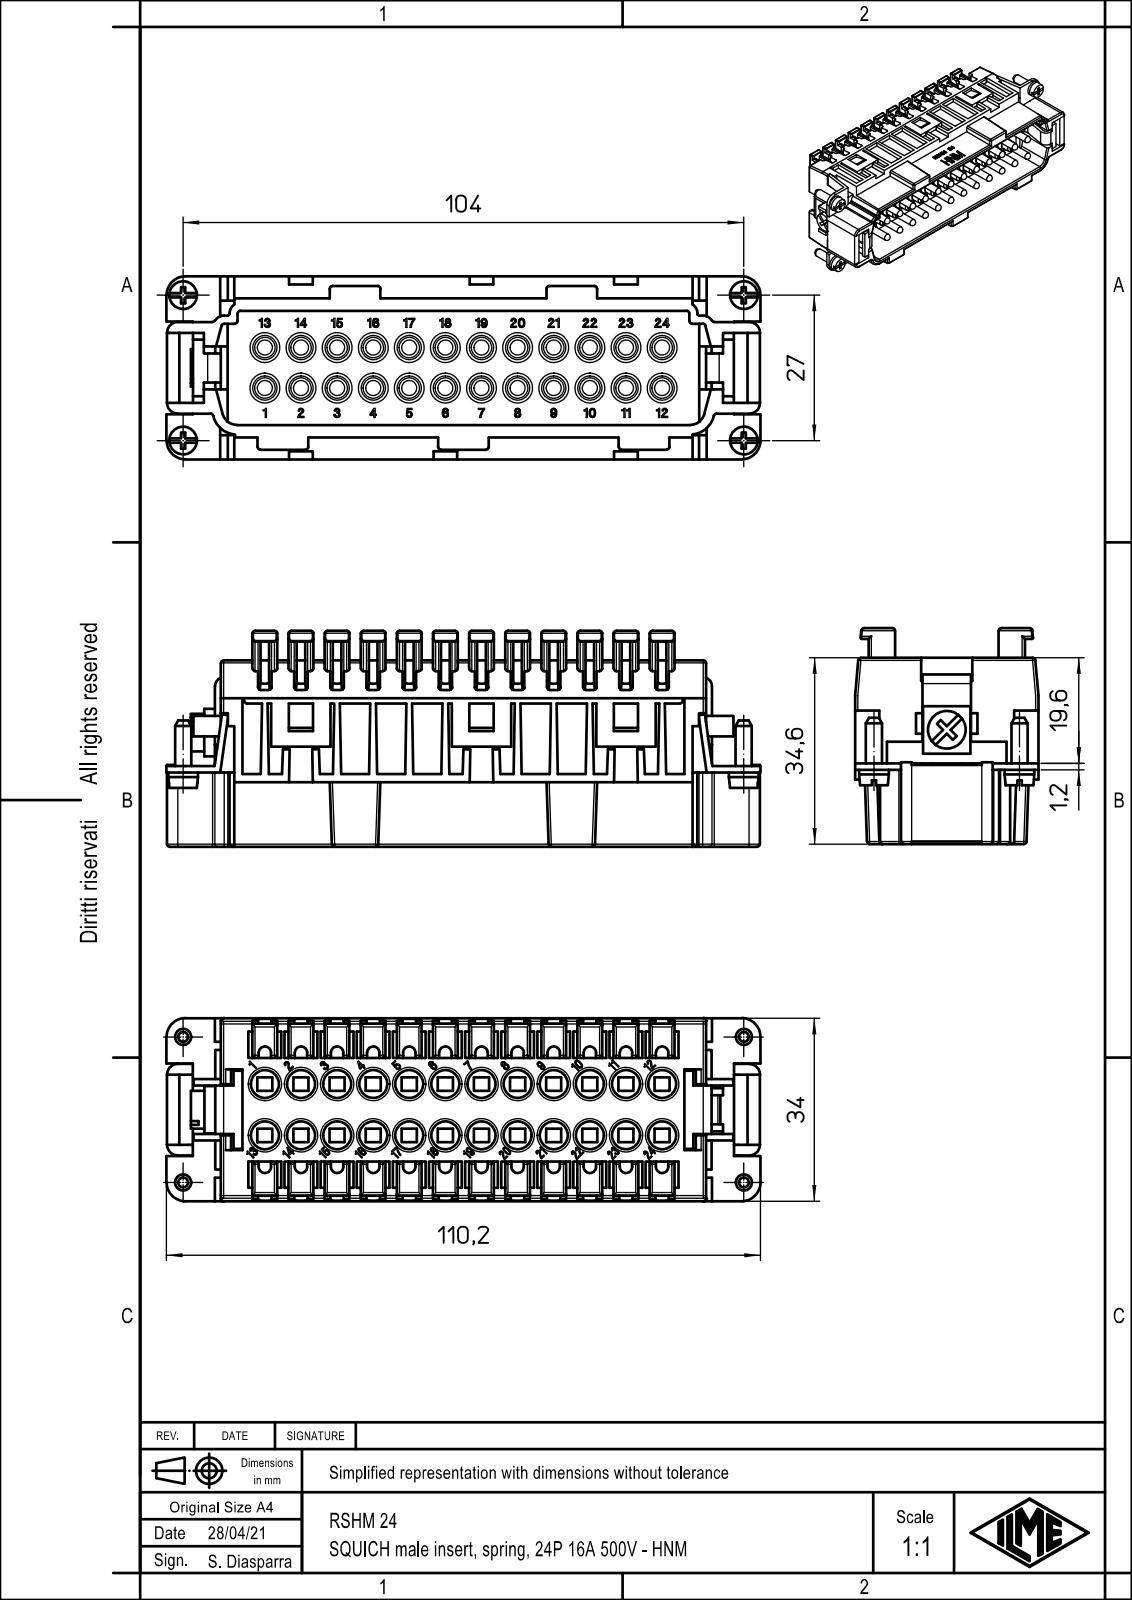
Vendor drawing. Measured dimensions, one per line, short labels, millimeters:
name: RSHM_24
written by: Creo Elements/Direct Modeling 20.1B 02-Apr-2019 (C) Parametric Technology GmbH (AUTOMOTIVE_DESIGN)
unit: mm
bodies: 1 solid, 2918 faces (1691 planar, 740 cylindrical, 487 other)
size: 110.2 × 40.1 × 34
volume: 71 429 mm³; area: 34 717 mm²
holes: 24× ⌀5.2, 1× ⌀3.3
bosses: 24× ⌀2.48, 4× ⌀5.5, 4× ⌀3, 1× ⌀7
rounds: 212× R0.5, 52× R0.3, 50× R0.2, 24× R1.15, 10× R2, 4× R3.5, 2× R1, 2× R1.3
face distances: 1.5, 26.1, 20.1, 4.9, 27.6, 6.4, 32.5, 2.5, 21.2, 25.1
hole spacings: 6.7, 11.62, 13.4, 16.43, 20.1, 22.23, 26.8, 28.43
